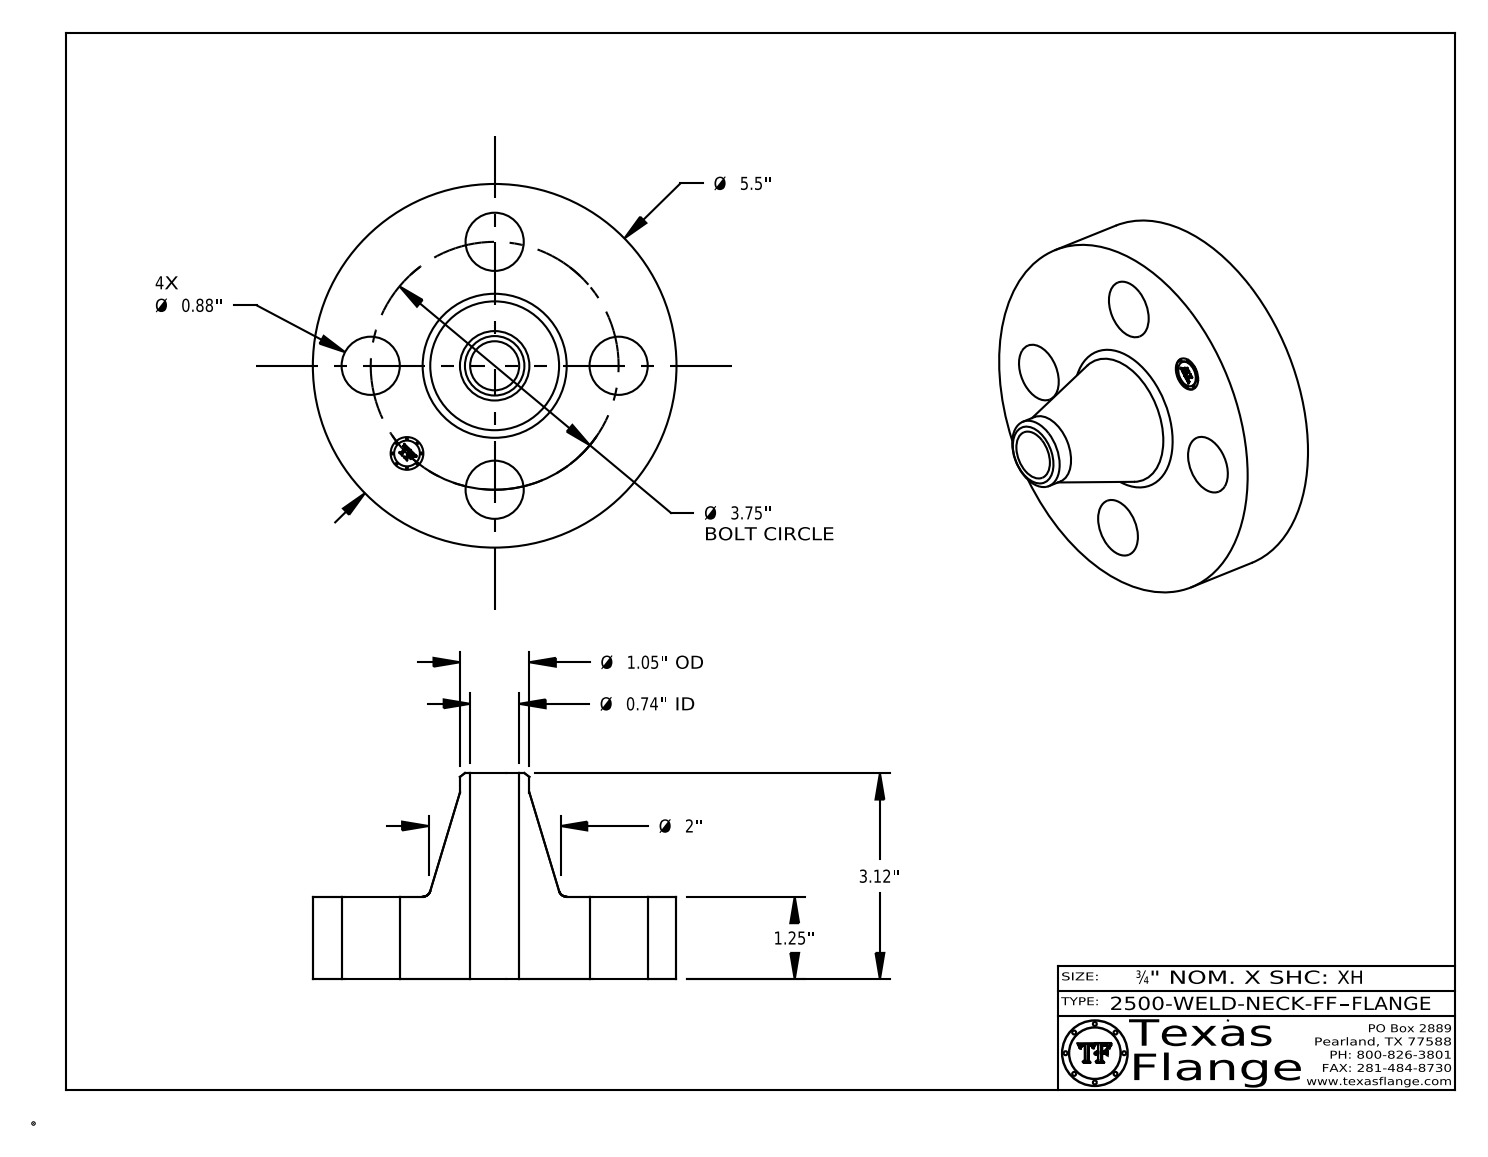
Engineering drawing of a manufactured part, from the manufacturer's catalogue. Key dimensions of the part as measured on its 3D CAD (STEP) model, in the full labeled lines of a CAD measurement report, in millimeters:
Part name (STEP PRODUCT): 2500-WELD-NECK-FF
STEP written by: CATIA V5 STEP AP214 (AUTOMOTIVE_DESIGN)
Units: millimetres
Bodies: 1 solid, 408 faces (368 planar, 34 cylindrical, 6 other)
Overall size (bounding box): 139.7 × 139.7 × 79.2
Volume: 467 700 mm³ · Surface area: 58 630 mm²
Round holes (diameter × count): ⌀22.4 ×4, ⌀12.6 ×1, ⌀18.8 ×1
Round bosses / shafts (diameter × count): ⌀0.8 ×8, ⌀139.7 ×1, ⌀26.7 ×1, ⌀9.9 ×1
Main face-to-face distances: 31.8, 79.2, 47.5, 31.4, 0.4, 47.9, 3.8, 3.7, 0.7, 2.4
Hole centre spacings: 47.6, 67.4, 36.4, 88, 95.3
